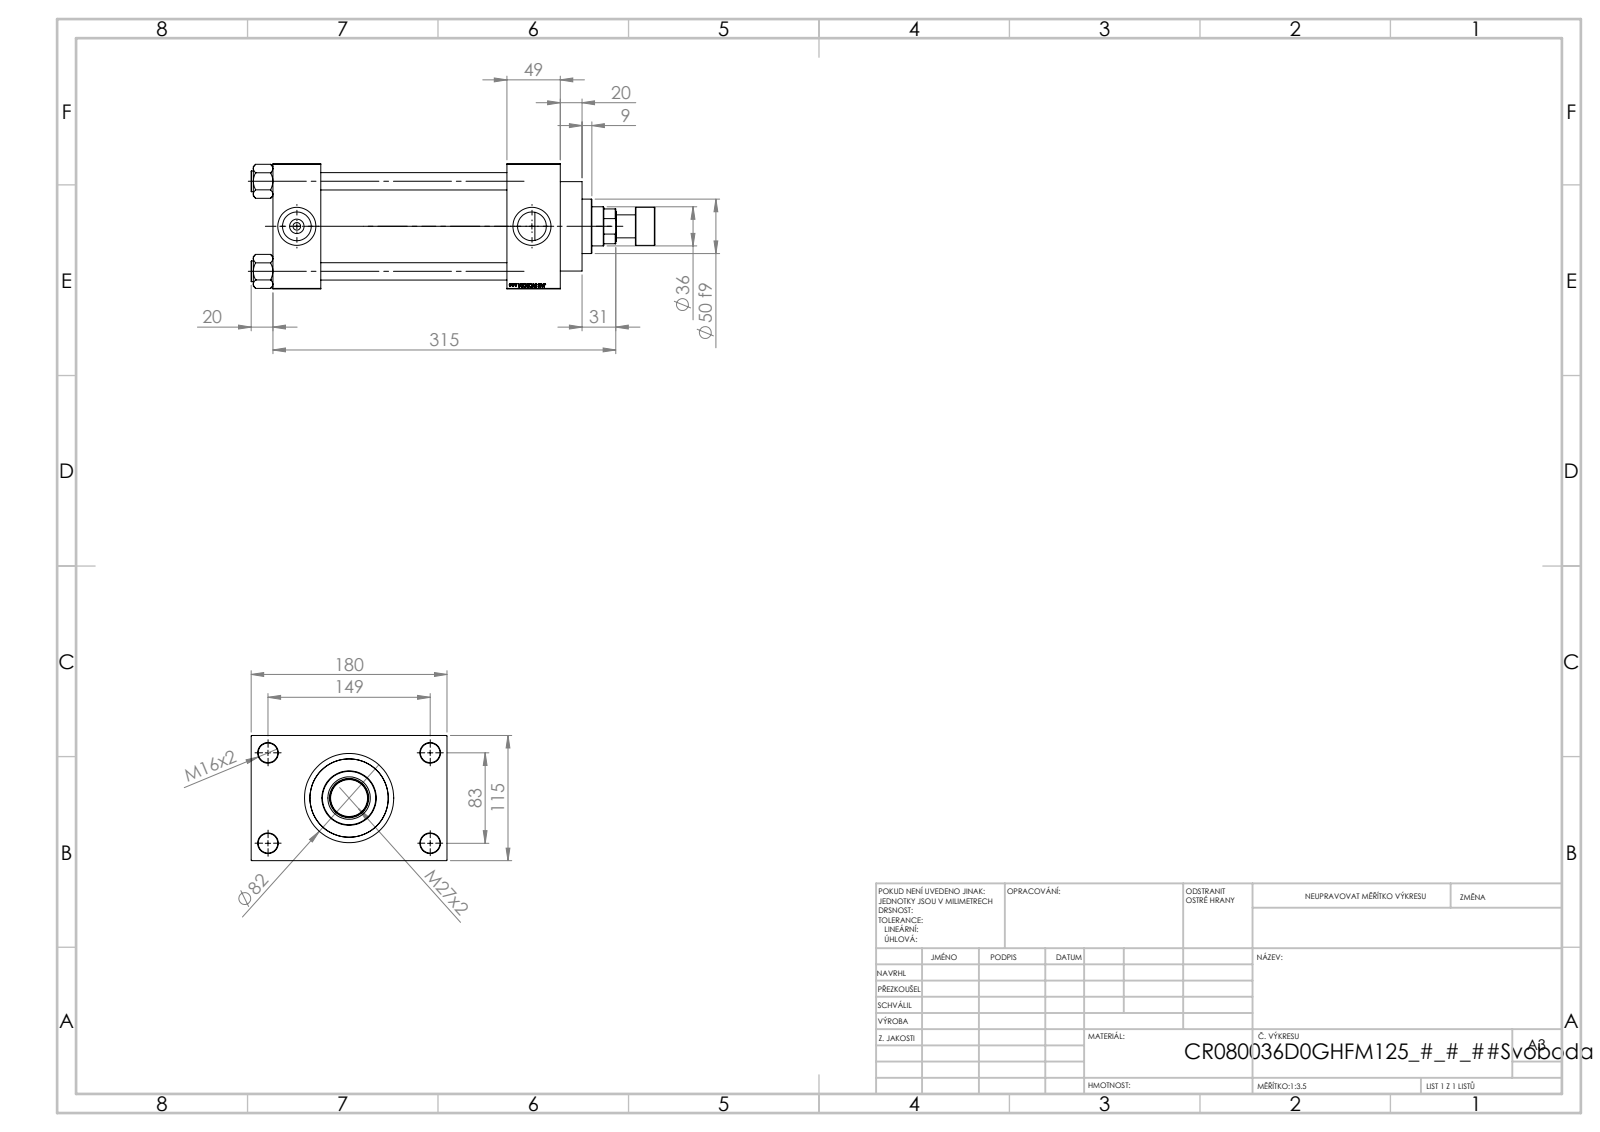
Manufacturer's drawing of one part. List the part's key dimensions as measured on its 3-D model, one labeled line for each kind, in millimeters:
Part name (STEP PRODUCT): V215CR_D_Body; V215_VC_A; NUT_M5_D; V215CR_VCP_D (+2 more)
STEP written by: SolidWorks 2019 (CONFIG_CONTROL_DESIGN)
Units: millimetres
Bodies: 12 solids, 1165 faces (549 planar, 92 cylindrical, 524 other)
Overall size (bounding box): 371 × 180 × 115
Volume: 2 277 000 mm³ · Surface area: 389 906 mm²
Round holes (diameter × count): ⌀16 ×4, ⌀18 ×4, ⌀7 ×2, ⌀26.44 ×2, ⌀35 ×2, ⌀25.5 ×1, ⌀36 ×1, ⌀39 ×1, ⌀61 ×1, ⌀72 ×1, ⌀80 ×1
Round bosses / shafts (diameter × count): ⌀19 ×4, ⌀86 ×1, ⌀82 ×1, ⌀50 ×1, ⌀35 ×1, ⌀21 ×1
Main face-to-face distances: 115, 171, 49, 220, 44, 215, 264, 32.5, 147.5, 180
Hole centre spacings: 33.15, 58.48, 82.7, 85.28, 89.24, 115.85, 142.43, 83
